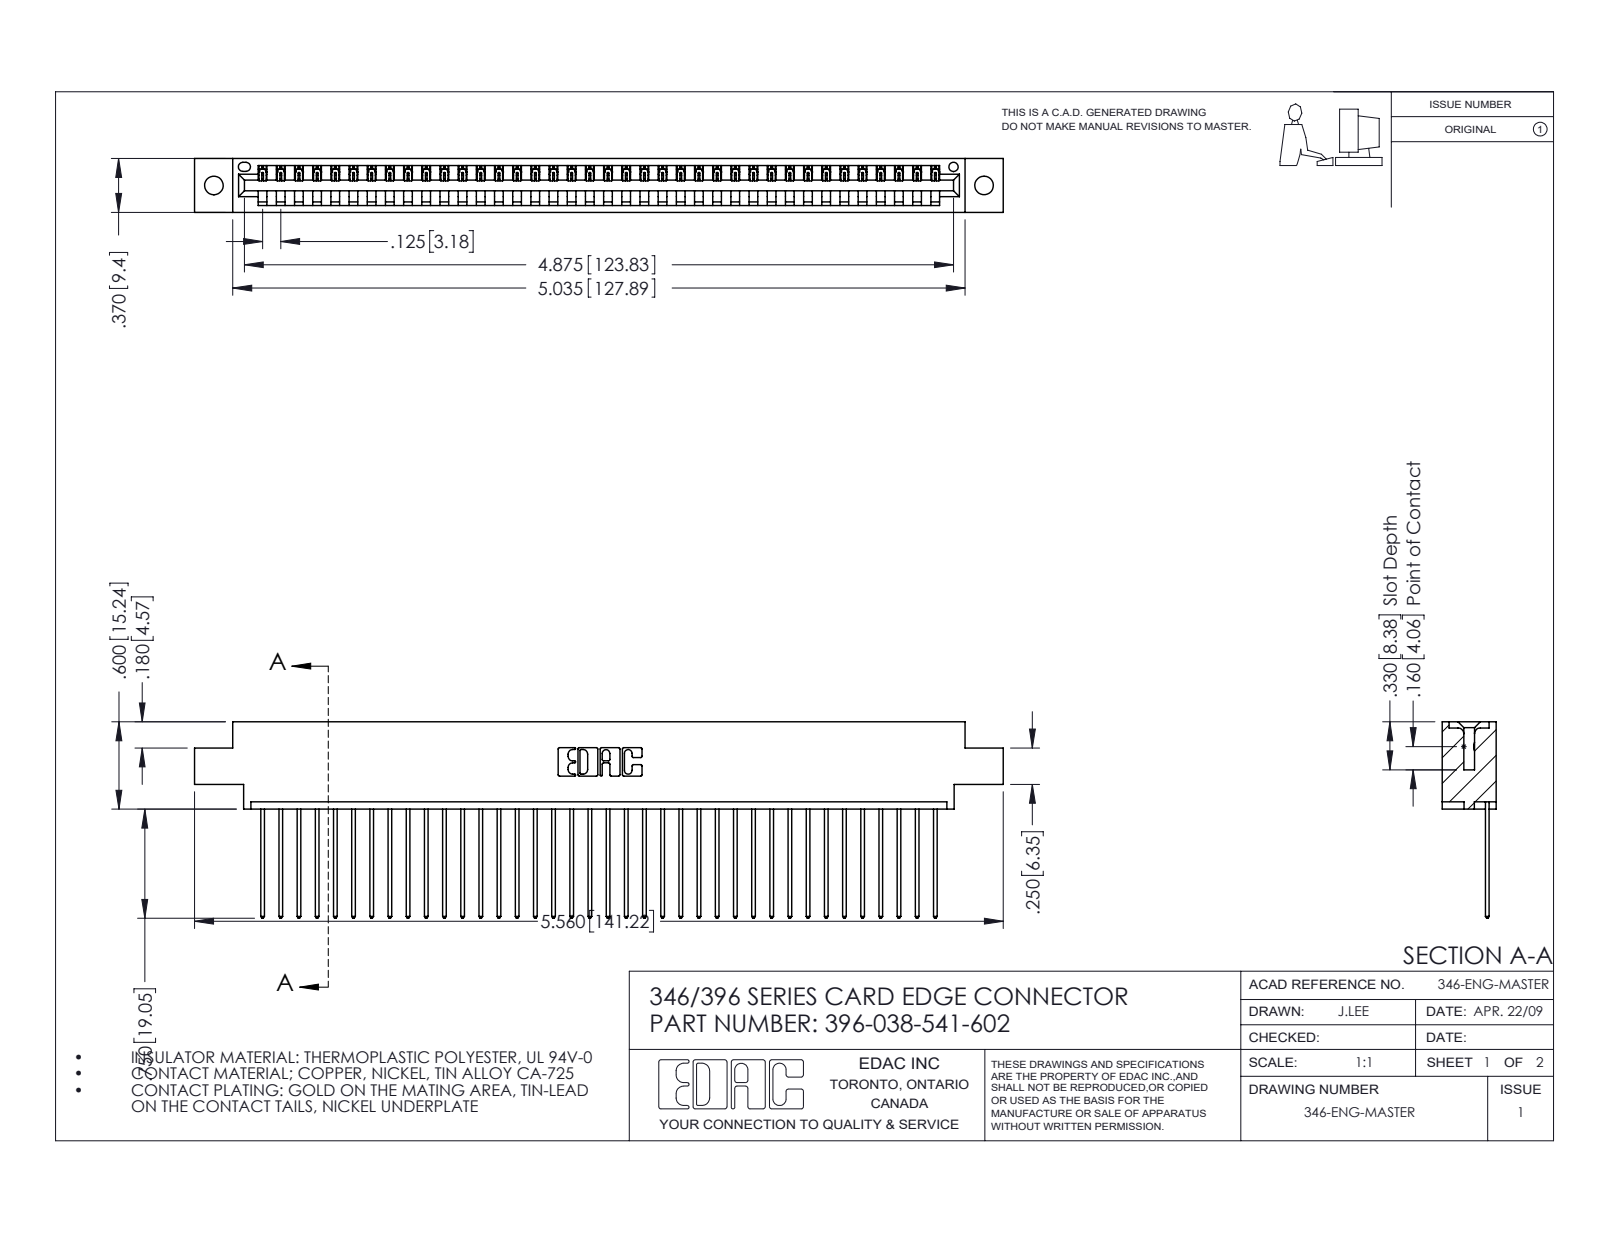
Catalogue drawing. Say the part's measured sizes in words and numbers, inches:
The part is named "396-038-541-602; 346 Part_0.170 Offset - 0.128 Dia; 345-292-001_345-293-141". Its 3-D file was written by "SolidWorks 2016 (CONFIG_CONTROL_DESIGN)". It is 39 solids with 2330 faces: 1600 planar, 730 cylindrical and 0 other. Overall it measures 5.56 by 1.35 by 0.37 inches. Its volume is 0.819 cubic inches and its surface area 26.93 square inches. Round holes: 2 of diameter 0.128, 1 of diameter 0.064. Partial cylindrical surfaces (rounded edges, fillets, slot ends): 76 of radius 0.006, 76 of radius 0.01, 22 of radius 0.01, 6 of radius 0.007, 6 of radius 0.031, 3 of radius 0.026, 2 of radius 0.031, 2 of radius 0.04. The main face-to-face distances are 0.048, 0.322, 0.37, 0.25, 0.072, 0.298, 0.025, 0.148, 0.222, 0.1. The hole center spacings are 0.246, 5.086, 5.295.
